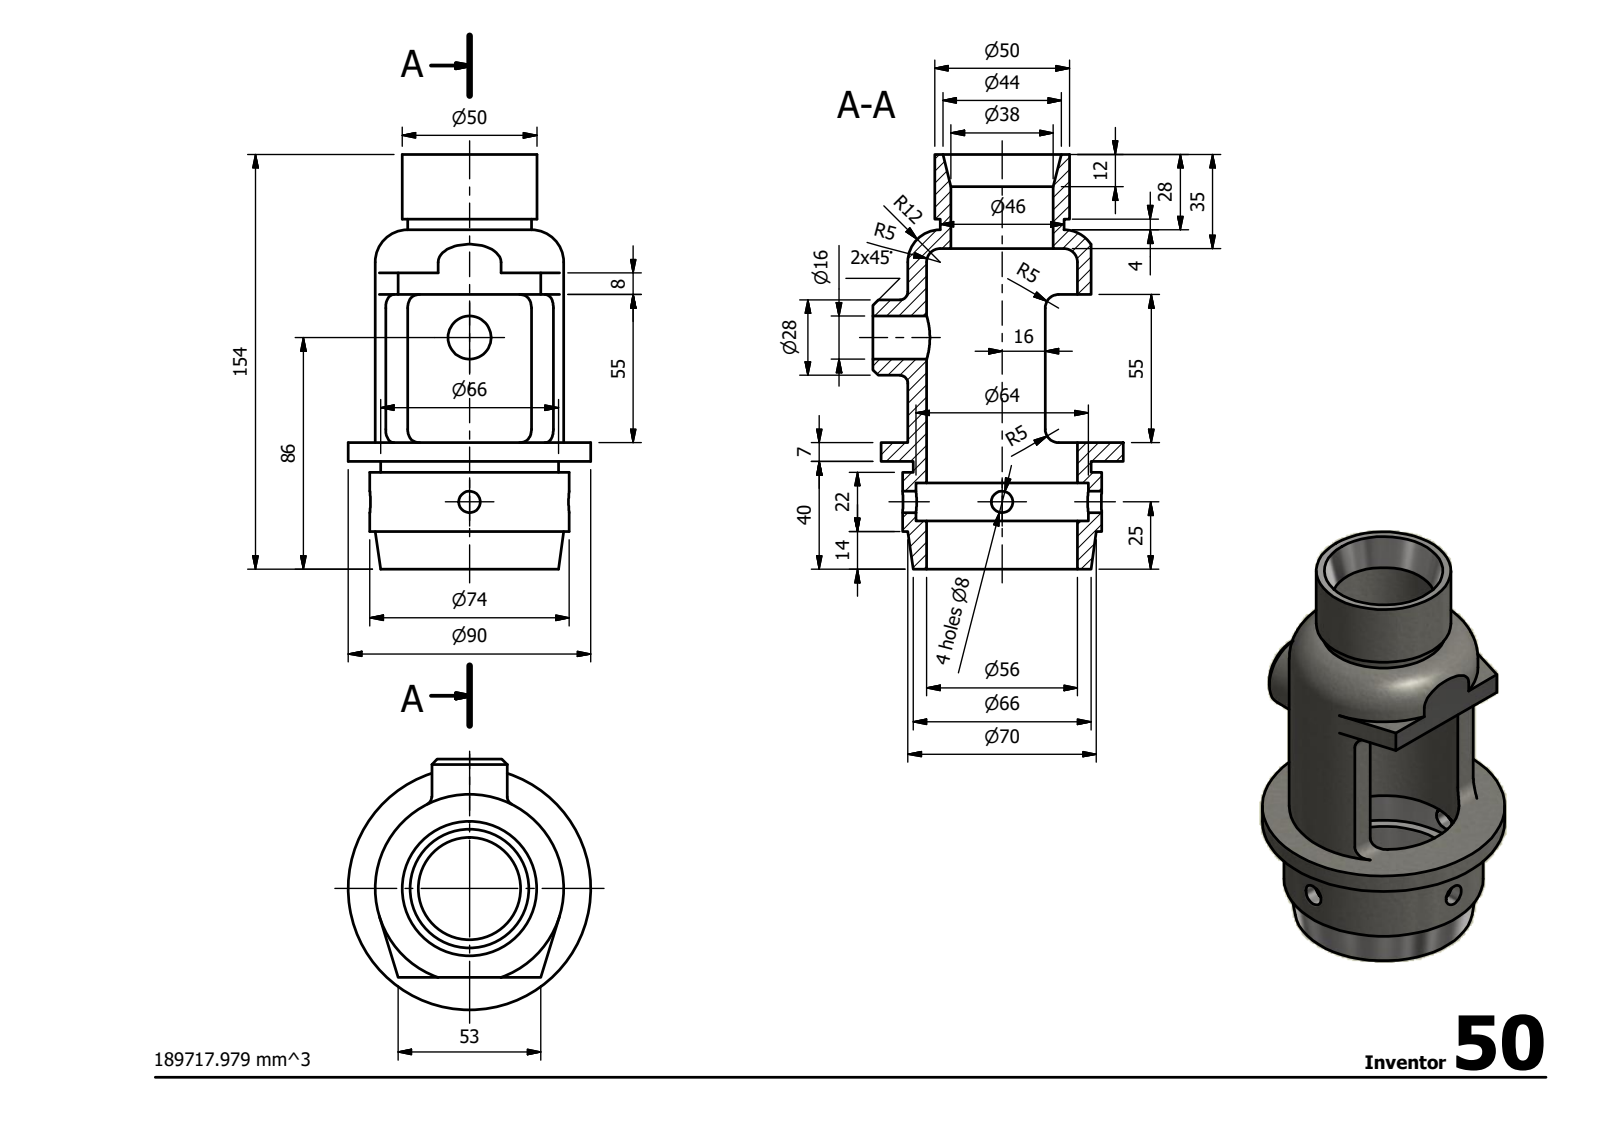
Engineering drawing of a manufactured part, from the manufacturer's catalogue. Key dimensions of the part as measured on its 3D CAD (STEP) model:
STEP written by: Autodesk Inventor 2014 (AUTOMOTIVE_DESIGN)
Units: millimetres
Bodies: 1 solid, 45 faces (19 planar, 20 cylindrical, 6 other)
Overall size (bounding box): 154 × 93 × 90
Volume: 189 756 mm³ · Surface area: 67 051 mm²
Round holes (diameter × count): ⌀8 ×2, ⌀16 ×1, ⌀38 ×1, ⌀56 ×1, ⌀64 ×1
Round bosses / shafts (diameter × count): ⌀90 ×1, ⌀74 ×1, ⌀70 ×1, ⌀66 ×1, ⌀50 ×1, ⌀46 ×1, ⌀28 ×1
Partial cylindrical surfaces — rounded edges, fillets, slot ends (radius × count): R5 ×2
Main face-to-face distances: 7, 4, 18, 22, 14, 11, 17, 40, 47, 8
Hole centre spacings: 61
